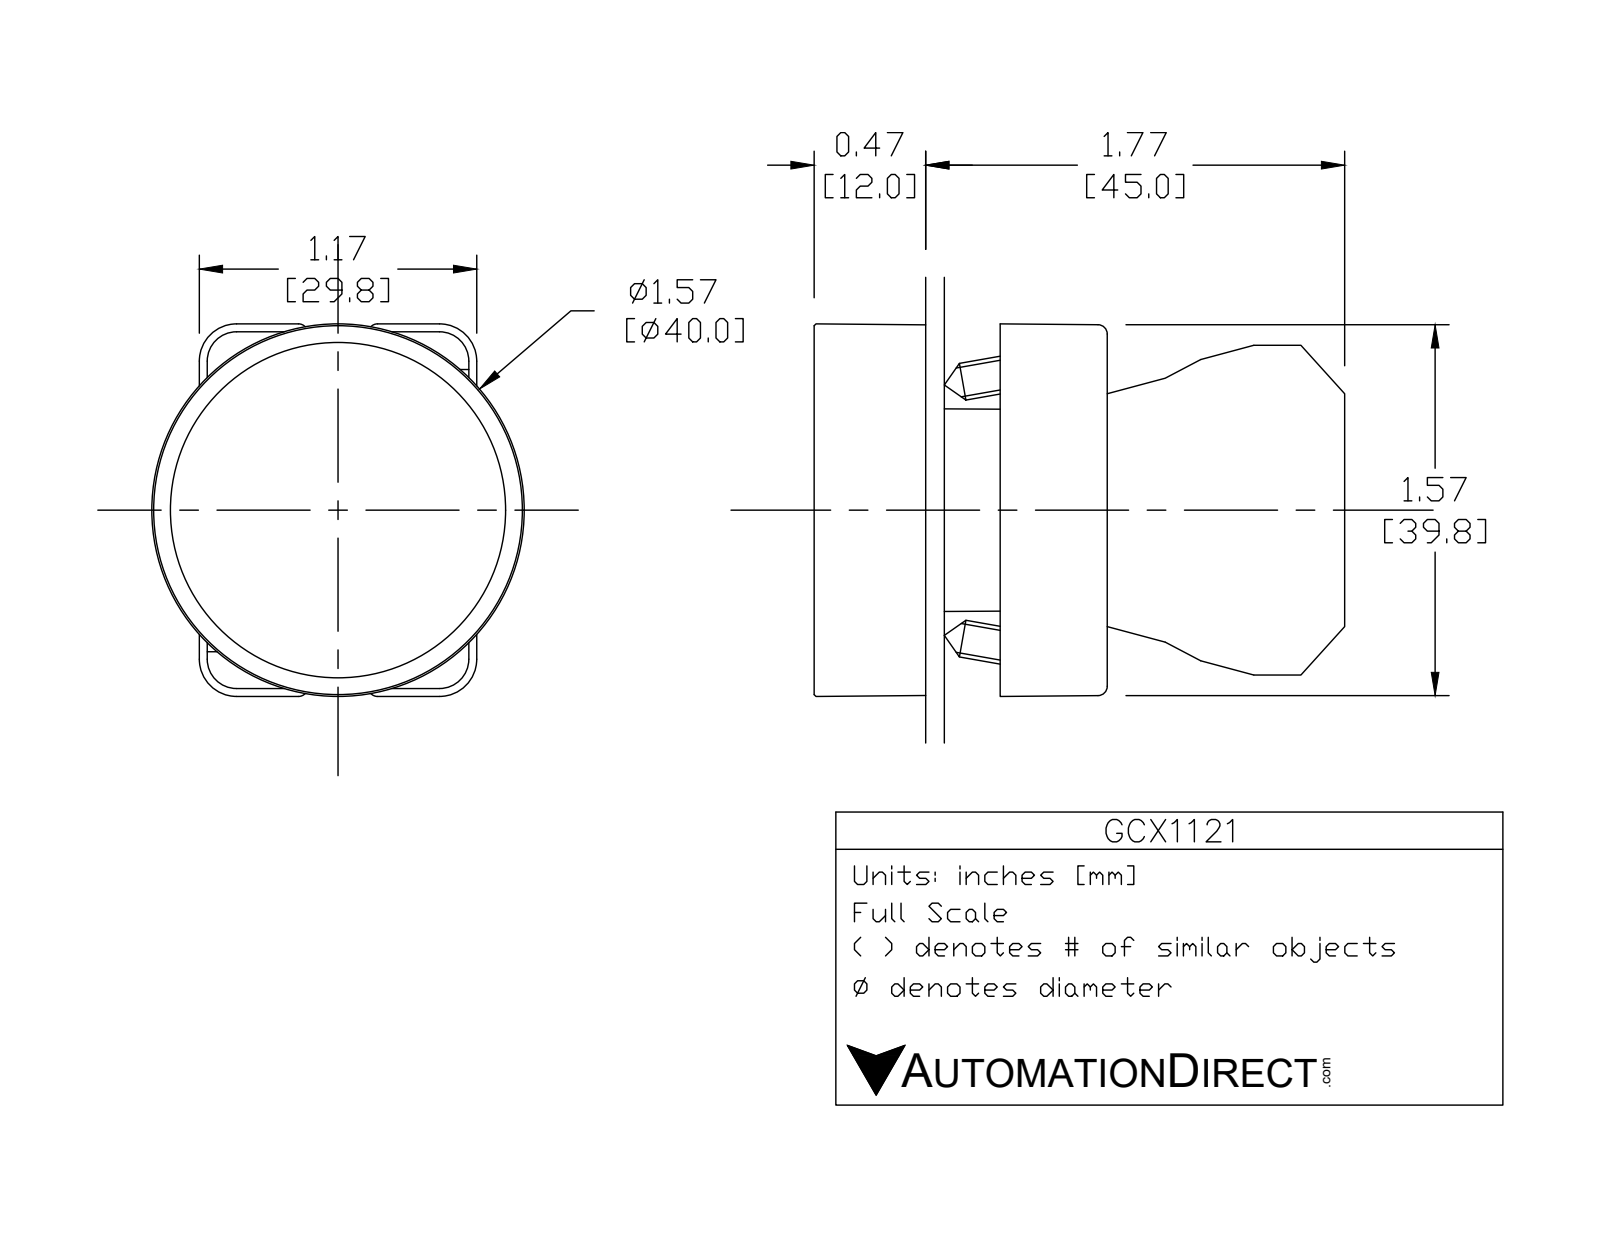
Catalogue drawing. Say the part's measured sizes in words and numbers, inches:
The part is named "ecx1040; GCX1121 OPERATOR; GCX1121; ecx1029". Its 3-D file was written by "SolidWorks 2016 (AUTOMOTIVE_DESIGN)". It is 6 solids with 381 faces: 222 planar, 132 cylindrical and 27 other. Overall it measures 2.217 by 1.581 by 1.575 inches. Its volume is 2.16 cubic inches and its surface area 32.13 square inches. Round holes: 2 of diameter 0.079, 2 of diameter 0.124, 2 of diameter 0.13, 1 of diameter 0.087, 1 of diameter 0.197, 1 of diameter 0.878, 1 of diameter 0.888, 1 of diameter 1.417. Round bosses or shafts: 2 of diameter 0.157, 1 of diameter 1.575, 1 of diameter 1.398, 1 of diameter 0.945, 1 of diameter 0.856, 1 of diameter 0.78. Partial cylindrical surfaces (rounded edges, fillets, slot ends): 24 of radius 0.059, 12 of radius 0.041, 12 of radius 0.124, 12 of radius 0.157, 4 of radius 0.039, 2 of radius 0.128, 1 of radius 0.02, 1 of radius 0.063. The main face-to-face distances are 0.472, 0.72, 1.193, 0.579, 0.7, 0.02, 0.493, 0.033, 0.031, 0.689. The hole center spacings are 0.236, 0.544, 0.472, 0.49.
